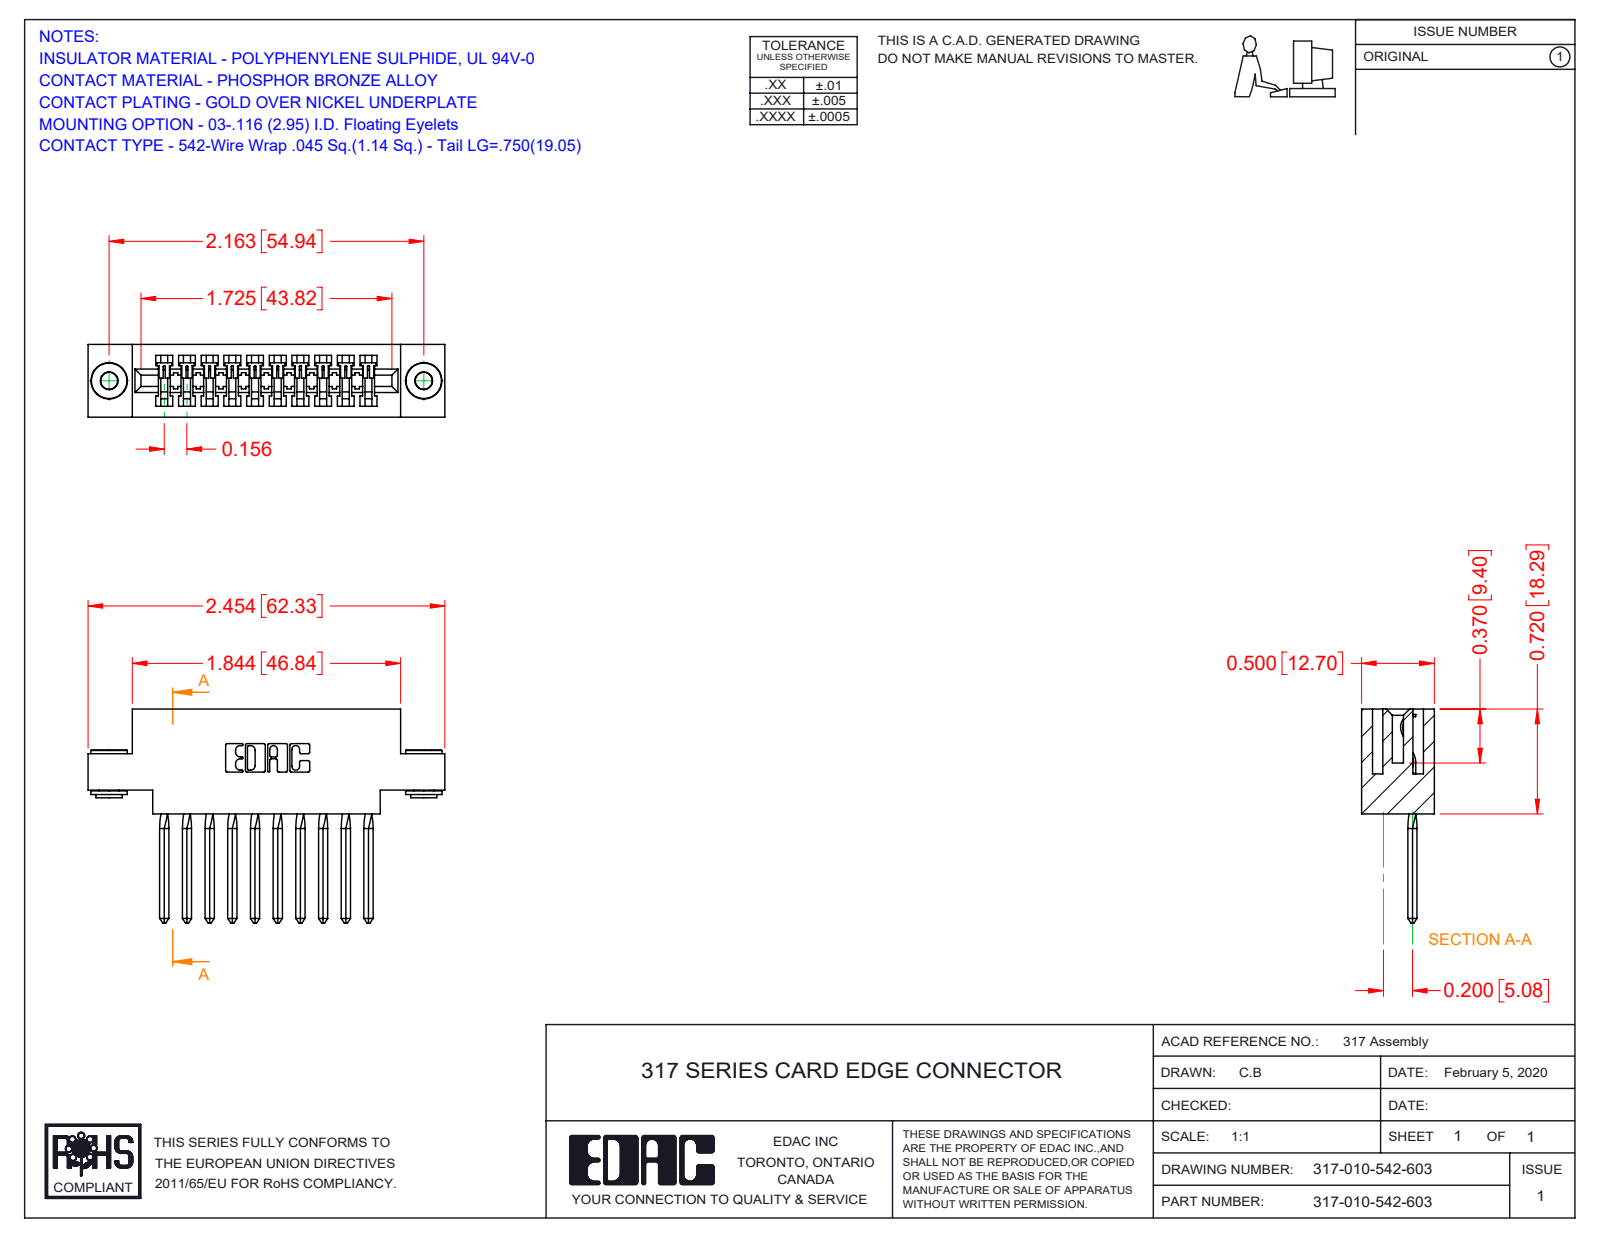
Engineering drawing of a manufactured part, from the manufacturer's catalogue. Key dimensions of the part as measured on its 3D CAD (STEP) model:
Part name (STEP PRODUCT): 317-010-542-603; 345-250-002_345-250-002-102; 317-290-003_542; 317 Part_.156 Dia - TH
STEP written by: SolidWorks 2016 (CONFIG_CONTROL_DESIGN)
Units: inches
Bodies: 13 solids, 890 faces (708 planar, 134 cylindrical, 48 other)
Overall size (bounding box): 2.454 × 1.47 × 0.5
Volume: 0.537 in³ · Surface area: 15.87 in²
Round holes (diameter × count): ⌀0.116 ×2, ⌀0.156 ×2
Round bosses / shafts (diameter × count): ⌀0.25 ×2, ⌀0.18 ×2, ⌀0.136 ×2
Partial cylindrical surfaces — rounded edges, fillets, slot ends (radius × count): R0.01 ×22, R0.006 ×20, R0.007 ×6, R0.031 ×6, R0.026 ×3, R0.074 ×1, R0.089 ×1, R0.1 ×1
Main face-to-face distances: 0.5, 0.075, 0.425, 0.11, 0.065, 0.22, 0.35, 0.331, 0.156, 0.116
Hole centre spacings: 2.163
